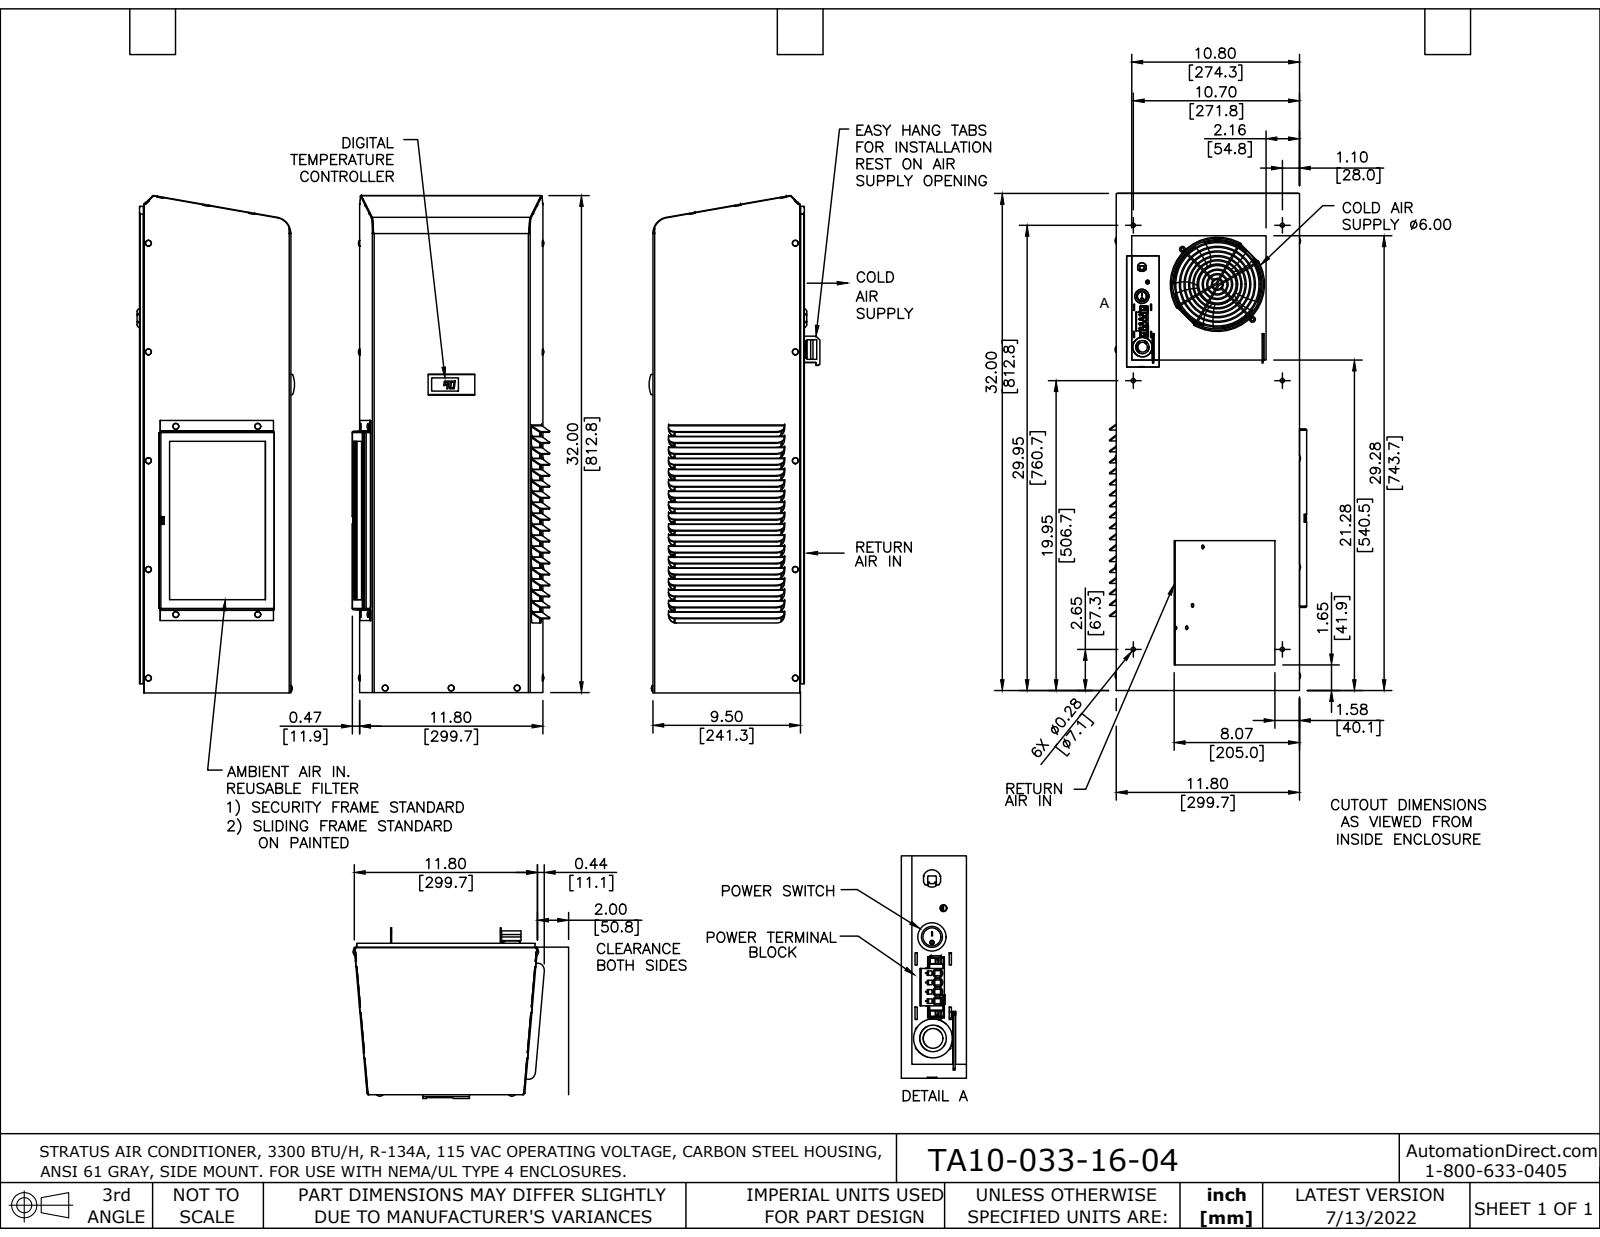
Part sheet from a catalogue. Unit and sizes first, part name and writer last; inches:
Units: inches
Overall size (bounding box): 32.024 × 12.576 × 11.549
Round holes (diameter × count): ⌀0.159 ×11, ⌀0.204 ×5, ⌀6 ×1
Round bosses / shafts (diameter × count): ⌀0.19 ×7, ⌀0.353 ×2, ⌀0.248 ×2, ⌀6.07 ×1, ⌀0.906 ×1, ⌀0.38 ×1, ⌀0.379 ×1, ⌀0.087 ×1
Partial cylindrical surfaces — rounded edges, fillets, slot ends (radius × count): R0.015 ×45, R0.01 ×42, R0.5 ×36, R0.506 ×36, R0.1 ×28, R0.058 ×21, R0.116 ×21, R0.03 ×13
Main face-to-face distances: 0.058, 9.435, 9.377, 0.058, 9.493, 0.09, 0.25, 0.308, 9.685, 9.743
Hole centre spacings: 7, 14, 21, 1.732, 5.3, 6.565, 10.869, 12.12
Volume: 136.5 in³ · Surface area: 3 197 in²
Bodies: 1 solid, 1750 faces (1081 planar, 499 cylindrical, 170 other)
Part name (STEP PRODUCT): TA10-033-16-04
STEP written by: SolidWorks 2021 (AUTOMOTIVE_DESIGN)
